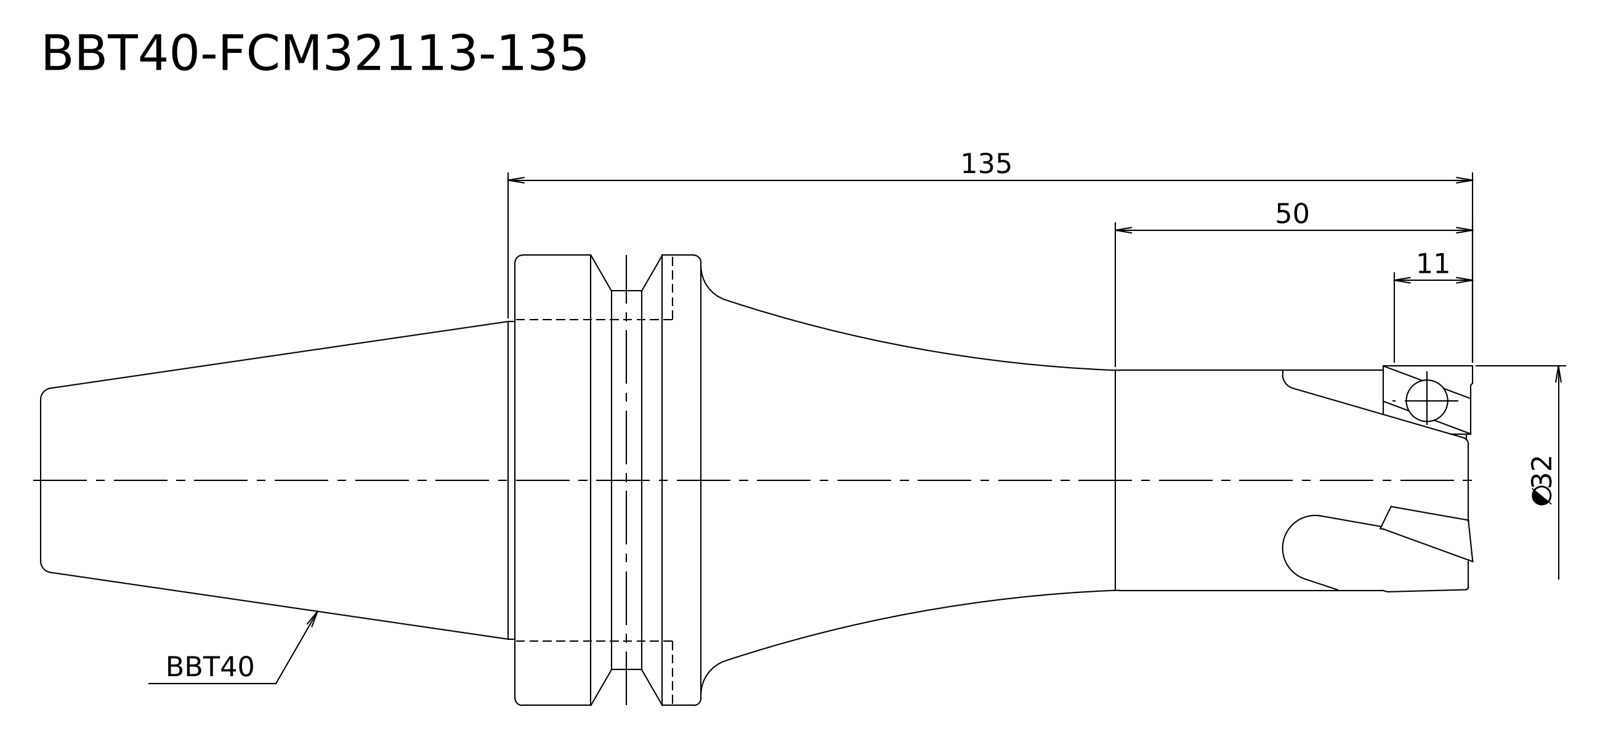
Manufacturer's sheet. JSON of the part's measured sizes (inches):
{"step_written_by": "Kubotek KeyCreator V8.5.1 (14335) (CONFIG_CONTROL_DESIGN)", "units": "inches", "bodies": {"solids": 1, "faces": 17, "planar": 5, "cylindrical": 6, "other": 6}, "overall_size": [7.89, 2.48, 2.48], "volume_in3": 15.76, "surface_area_in2": 45.75, "round_bosses_or_shafts": [[2.48, 1], [2.087, 1], [1.75, 1], [1.26, 1], [1.213, 1]], "face_to_face_distances": [5.276, 7.89, 2.614, 4.252, 1.024, 3.638, 1.969, 2.283, 3.307, 5.921]}
